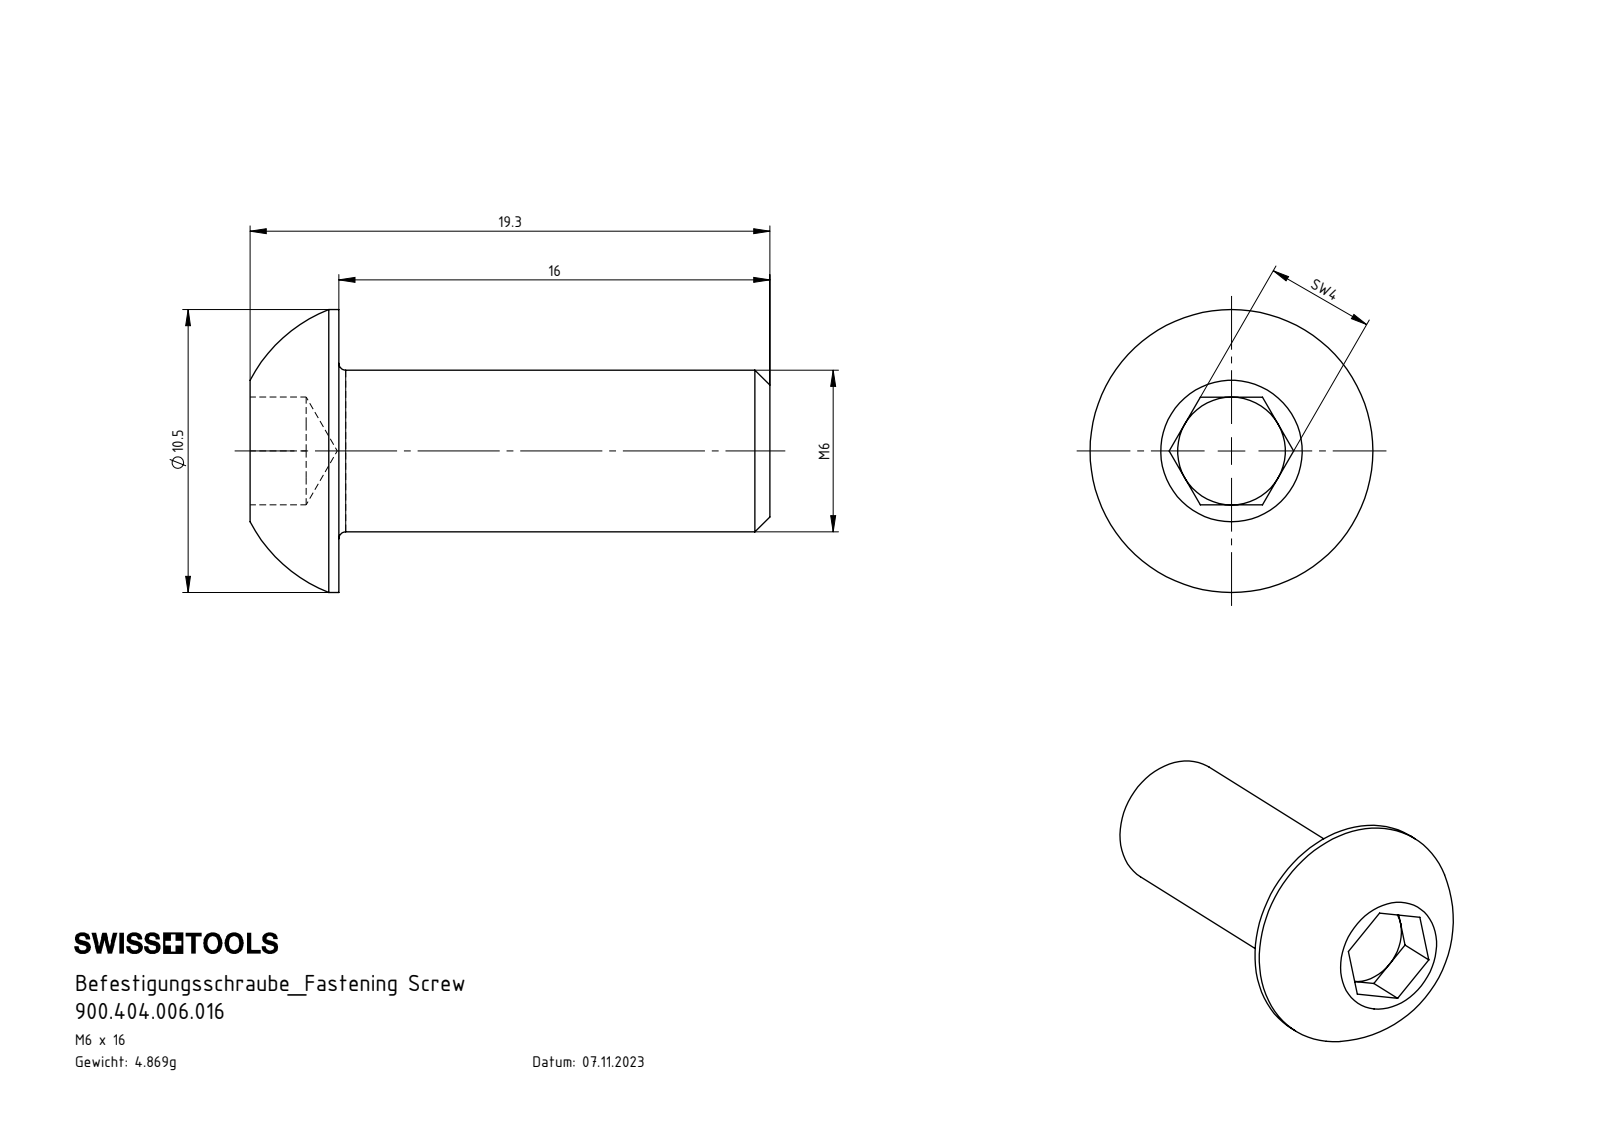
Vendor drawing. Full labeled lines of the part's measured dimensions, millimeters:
Part name (STEP PRODUCT): 900.404.006.016
STEP written by: SolidWorks 2022 (AUTOMOTIVE_DESIGN)
Units: millimetres
Bodies: 1 solid, 27 faces (15 planar, 4 cylindrical, 8 other)
Overall size (bounding box): 19.3 × 10.5 × 10.5
Volume: 620 mm³ · Surface area: 548 mm²
Round bosses / shafts (diameter × count): ⌀10.5 ×1, ⌀6 ×1
Main face-to-face distances: 16, 4, 3.3, 19.3, 2.08, 1.22, 17.22
